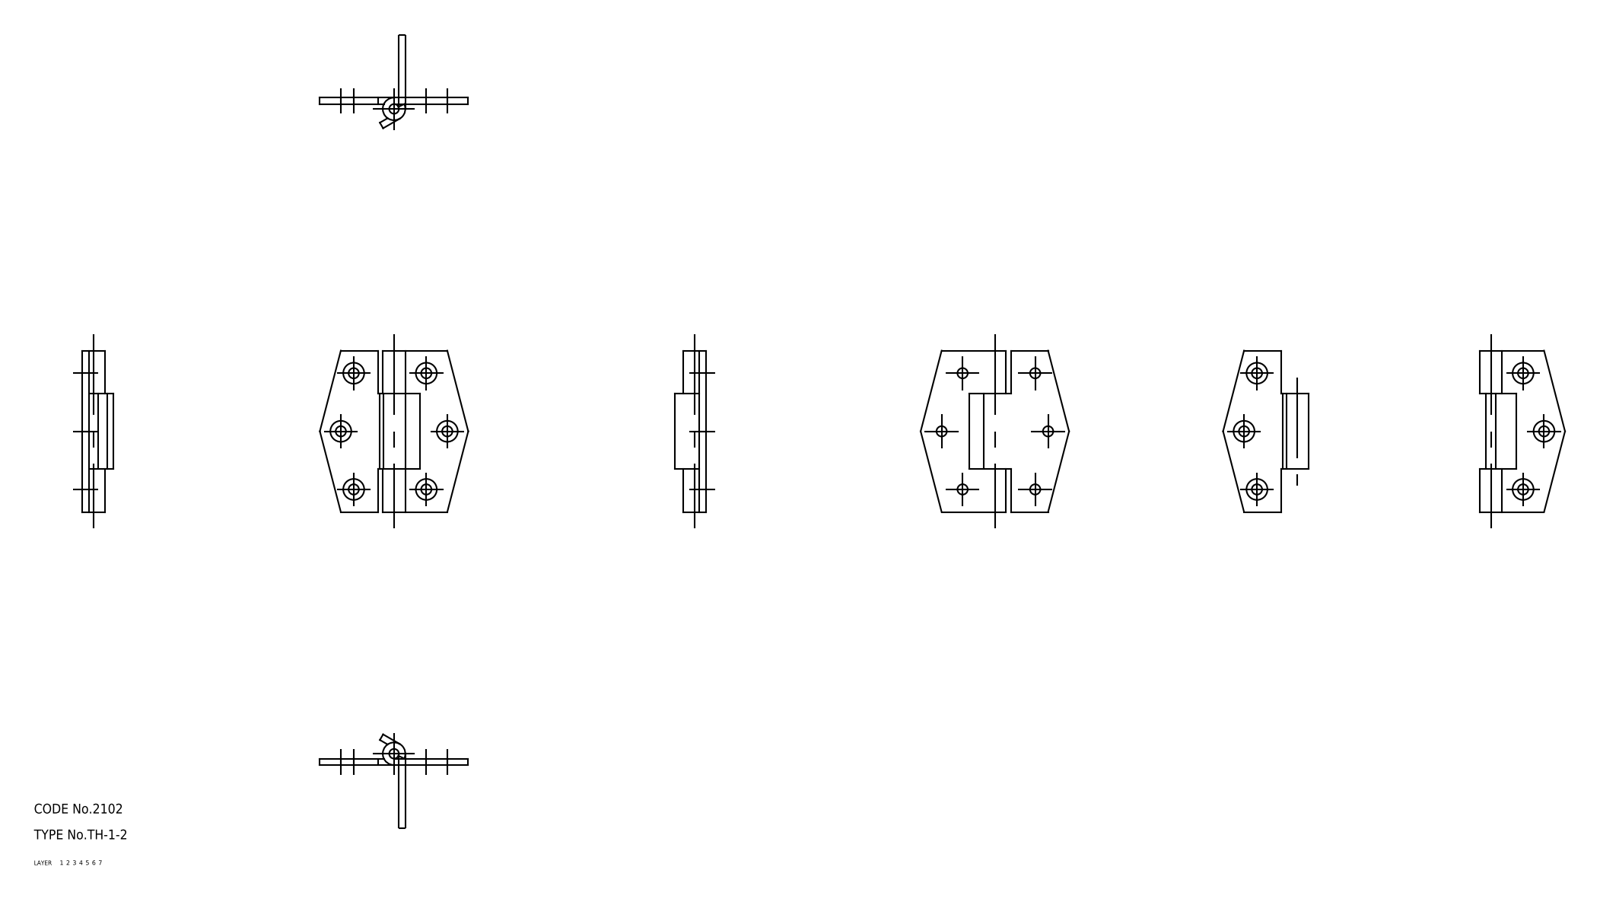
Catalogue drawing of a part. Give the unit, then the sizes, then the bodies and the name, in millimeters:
Units: millimetres
Overall size (bounding box): 50 × 46 × 9.5
Volume: 4 724 mm³ · Surface area: 5 773 mm²
Bodies: 3 solids, 58 faces (0 planar, 0 cylindrical, 58 other)
Part name (STEP PRODUCT): shaft; hinge piece_B; hinge piece_A; TH_1_2_349_36
STEP written by: CADfix (AUTOMOTIVE_DESIGN)
